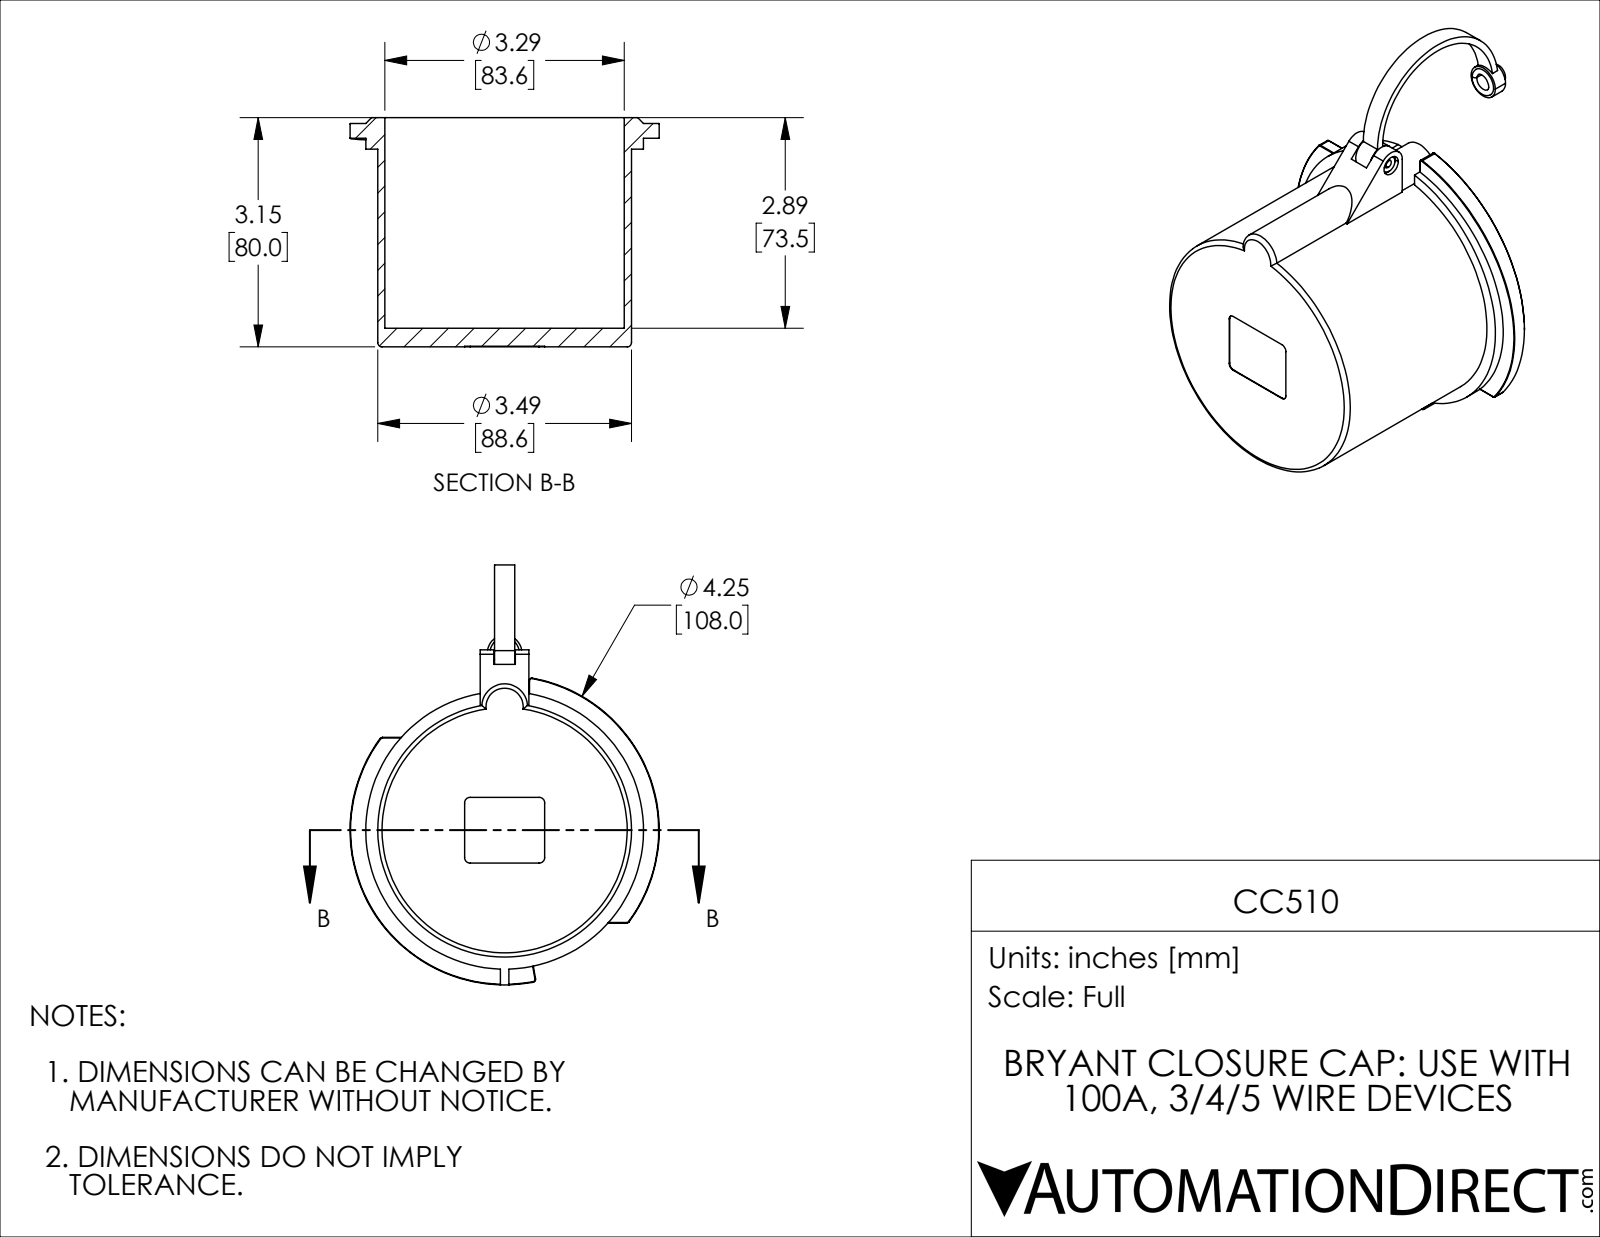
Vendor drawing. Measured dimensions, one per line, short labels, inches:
name: CC510
written by: SolidWorks 2021 (CONFIG_CONTROL_DESIGN)
unit: in
bodies: 1 solid, 149 faces (41 planar, 76 cylindrical, 32 other)
size: 5.771 × 4.684 × 4.252
volume: 7.112 in³; area: 99.82 in²
holes: 1× ⌀0.118, 1× ⌀0.169, 1× ⌀0.197, 1× ⌀0.244, 1× ⌀0.276, 1× ⌀3.291
bosses: 1× ⌀3.819, 1× ⌀3.488, 1× ⌀0.472, 1× ⌀0.433, 1× ⌀0.276, 1× ⌀0.236, 1× ⌀0.157
rounds: 8× R0.008, 4× R0.039, 4× R0.079, 1× R0.197, 1× R0.315, 1× R1.074, 1× R1.173, 1× R2.126
face distances: 0.256, 0.079, 2.894, 3.15, 2.815, 3.071, 0.354, 0.433, 2.461, 2.717
hole spacings: 2.441
